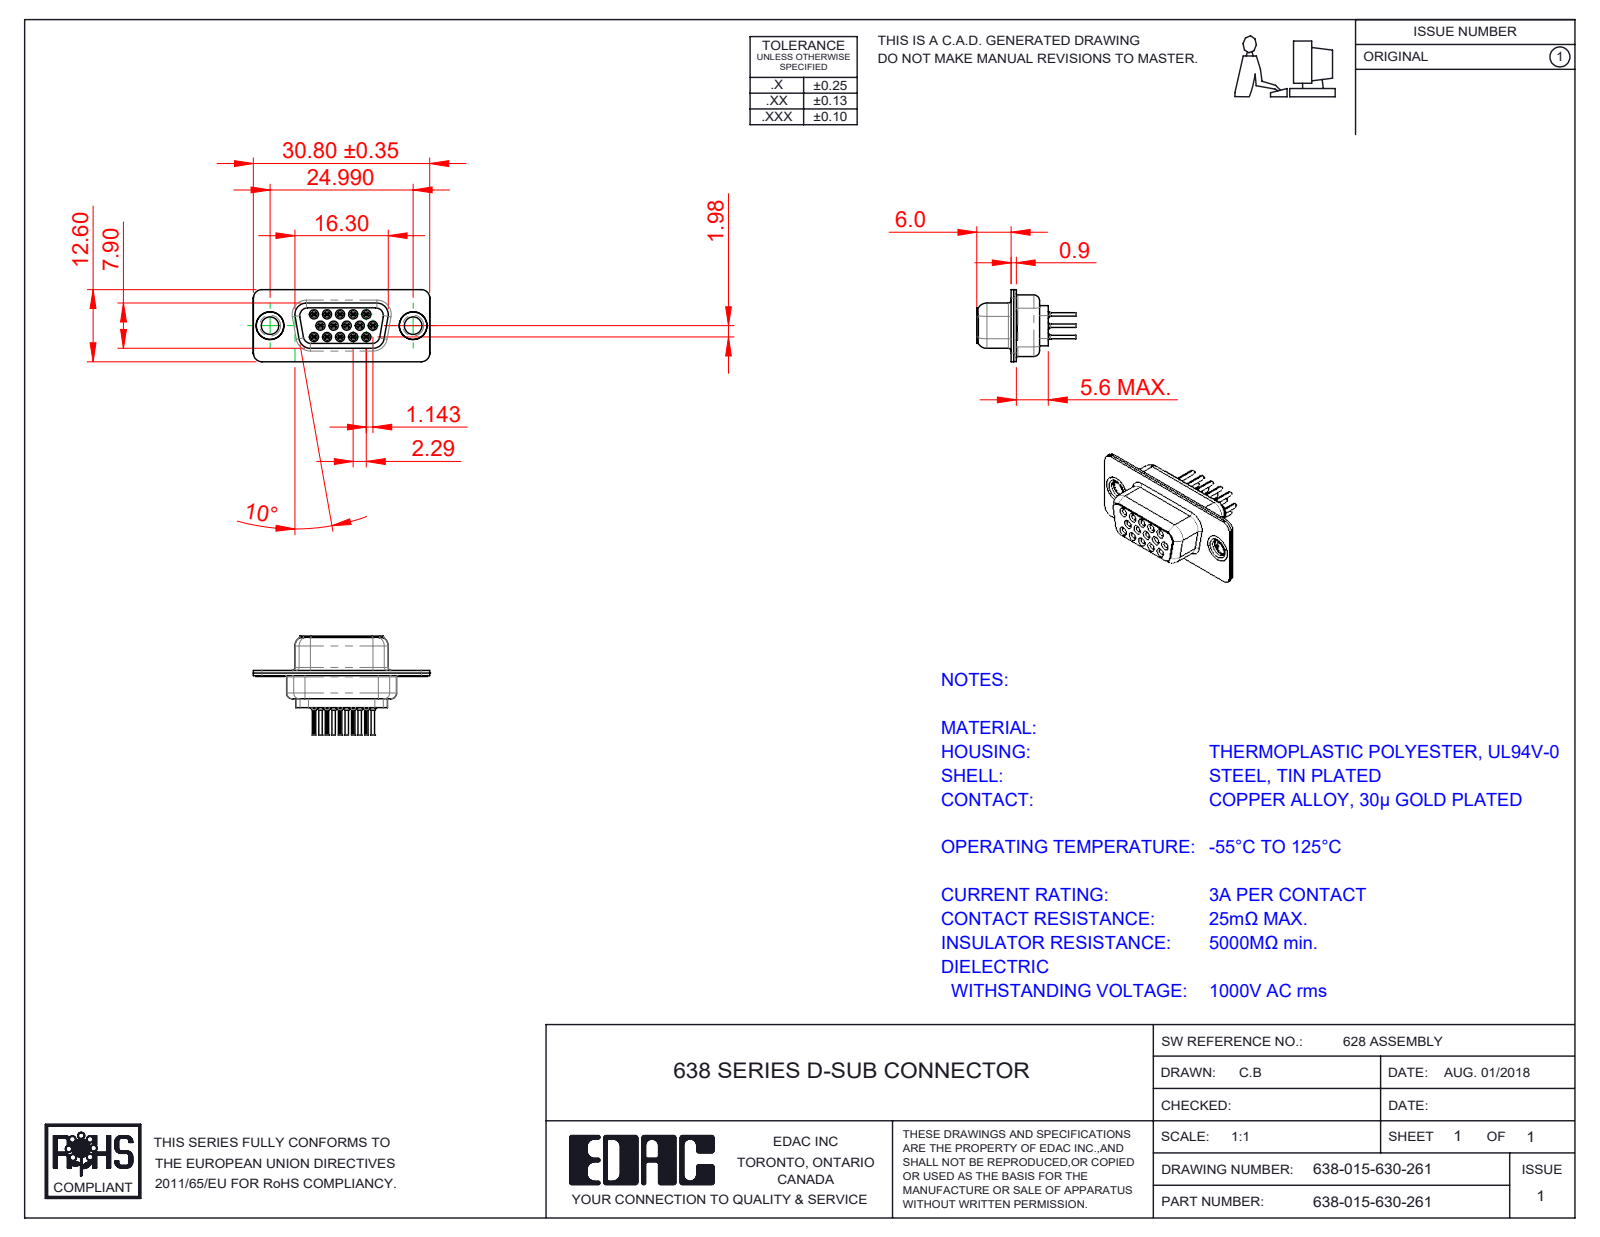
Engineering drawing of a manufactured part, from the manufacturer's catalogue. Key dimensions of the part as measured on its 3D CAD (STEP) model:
Part name (STEP PRODUCT): 638 Contact Row 1_30; 638 Shell Rear_15 Contacts; 638 Contact Row 2_30; 638 Contact Row 3_30 (+4 more)
STEP written by: SolidWorks 2020 (CONFIG_CONTROL_DESIGN)
Units: millimetres
Bodies: 20 solids, 2158 faces (532 planar, 616 cylindrical, 1010 other)
Overall size (bounding box): 30.81 × 17.3 × 12.6
Volume: 1 498 mm³ · Surface area: 5 452 mm²
Round holes (diameter × count): ⌀0.2 ×15, ⌀0.8 ×15, ⌀1 ×15, ⌀1.1 ×15, ⌀1.6 ×15, ⌀1.7 ×15, ⌀1.8 ×15, ⌀2 ×2, ⌀3.05 ×2, ⌀4 ×2, ⌀4.05 ×2, ⌀4.85 ×2
Round bosses / shafts (diameter × count): ⌀2 ×15, ⌀1.5 ×15, ⌀1.2 ×15, ⌀0.6 ×15, ⌀5 ×2, ⌀4.95 ×2, ⌀4.8 ×2, ⌀3.55 ×2
Partial cylindrical surfaces — rounded edges, fillets, slot ends (radius × count): R0.1 ×30, R1.5 ×20, R2 ×12, R0.28 ×10, R1.55 ×8, R1.35 ×5, R0.25 ×4, R0.5 ×4
Main face-to-face distances: 0.45, 0.9, 0.4, 1.43, 8.88, 6.6, 1.4, 2.28, 7.05, 6.05
Hole centre spacings: 3.96, 2.28, 4.57, 2.29, 6.05, 6.04, 6.86, 7.92
